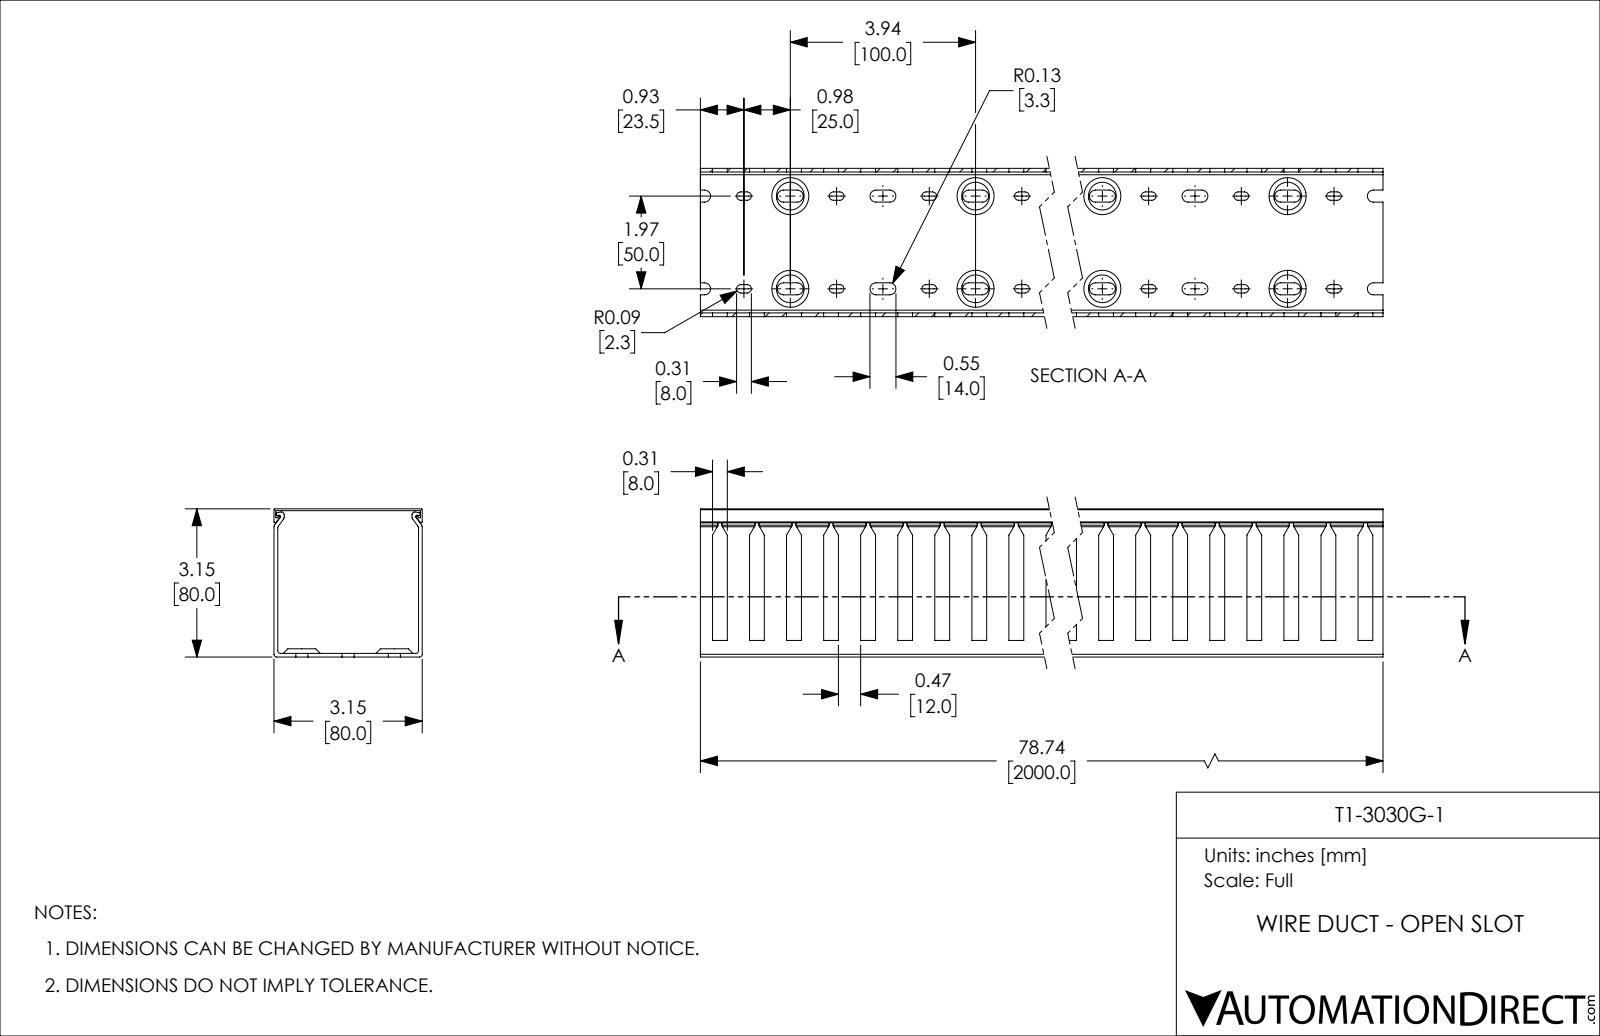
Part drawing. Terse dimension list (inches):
name: T1-3030G-1
written by: SolidWorks 2021 (CONFIG_CONTROL_DESIGN)
unit: in
bodies: 2 solids, 1573 faces (762 planar, 731 cylindrical, 80 other)
size: 78.74 × 3.15 × 3.15
volume: 68.59 in³; area: 2 052 in²
rounds: 200× R0.128, 160× R0.089, 12× R0.059, 8× R0.02, 6× R0.03
face distances: 0.079, 3.071, 3.15, 0.039, 3.11, 3.031, 2.992, 0.177, 2.933, 0.217
